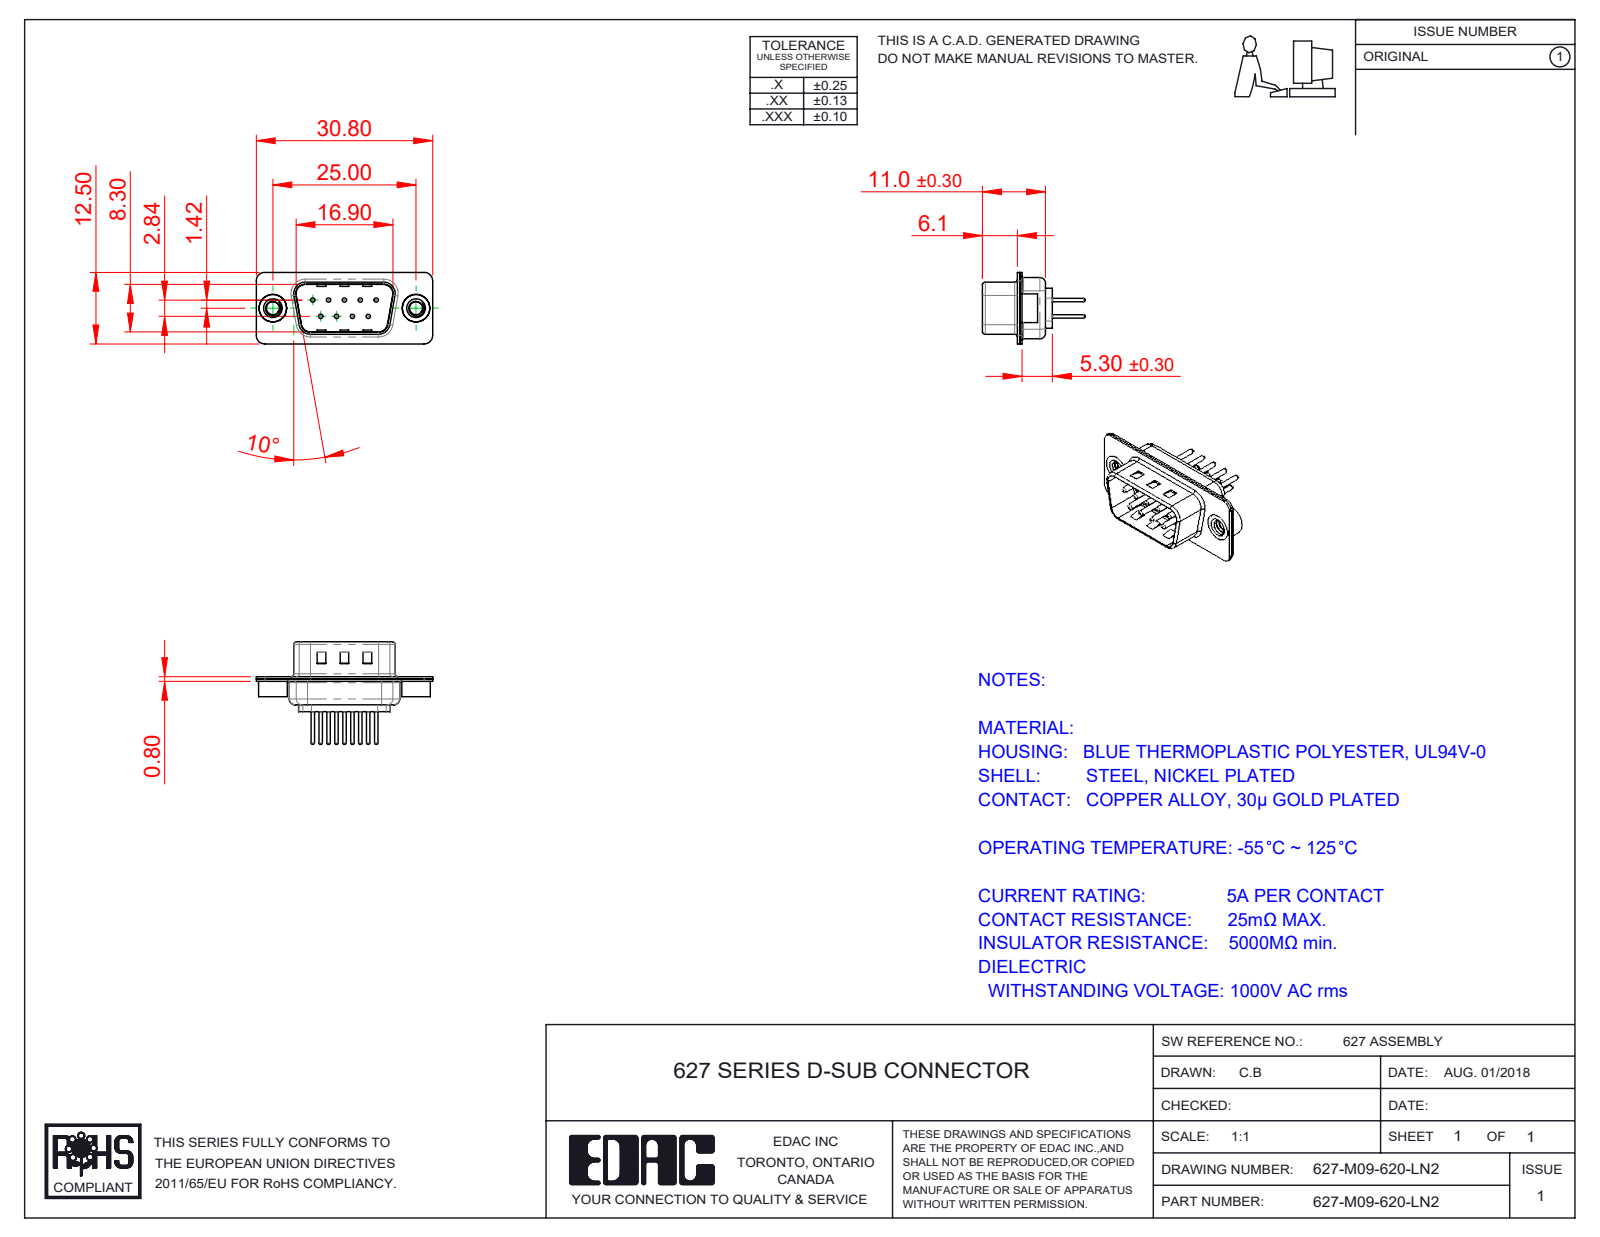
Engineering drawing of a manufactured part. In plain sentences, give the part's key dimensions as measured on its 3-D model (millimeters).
The part is named "627M 4-40 Threaded Rivet; 627M Contact Row 2_20; 627M Housing_09 Contacts; 627M Shell Rear_09 Contacts (+3 more)". Its 3-D file was written by "SolidWorks 2020 (CONFIG_CONTROL_DESIGN)". It is 14 solids with 637 faces: 170 planar, 255 cylindrical and 212 other. Overall it measures 30.8 by 17.9 by 12.5 millimeters. Its volume is 1 310 cubic millimeters and its surface area 3 574 square millimeters. Round holes: 9 of diameter 0.75, 9 of diameter 1.6, 9 of diameter 2, 2 of diameter 2.26, 2 of diameter 4, 2 of diameter 4.8. Round bosses or shafts: 9 of diameter 1.5, 9 of diameter 0.6, 2 of diameter 5, 2 of diameter 4.9. Partial cylindrical surfaces (rounded edges, fillets, slot ends): 16 of radius 1.5, 12 of radius 2, 8 of radius 0.5, 8 of radius 1.6, 4 of radius 0.25, 4 of radius 0.6, 4 of radius 0.65, 4 of radius 0.9. The main face-to-face distances are 0.4, 0.8, 9.5, 9.1, 8.7, 0.65, 9.9, 1.2, 6.1, 5.7. The hole center spacings are 3.16, 2.77, 5.54, 5.03, 5.04, 8.31, 7.1, 7.48.
